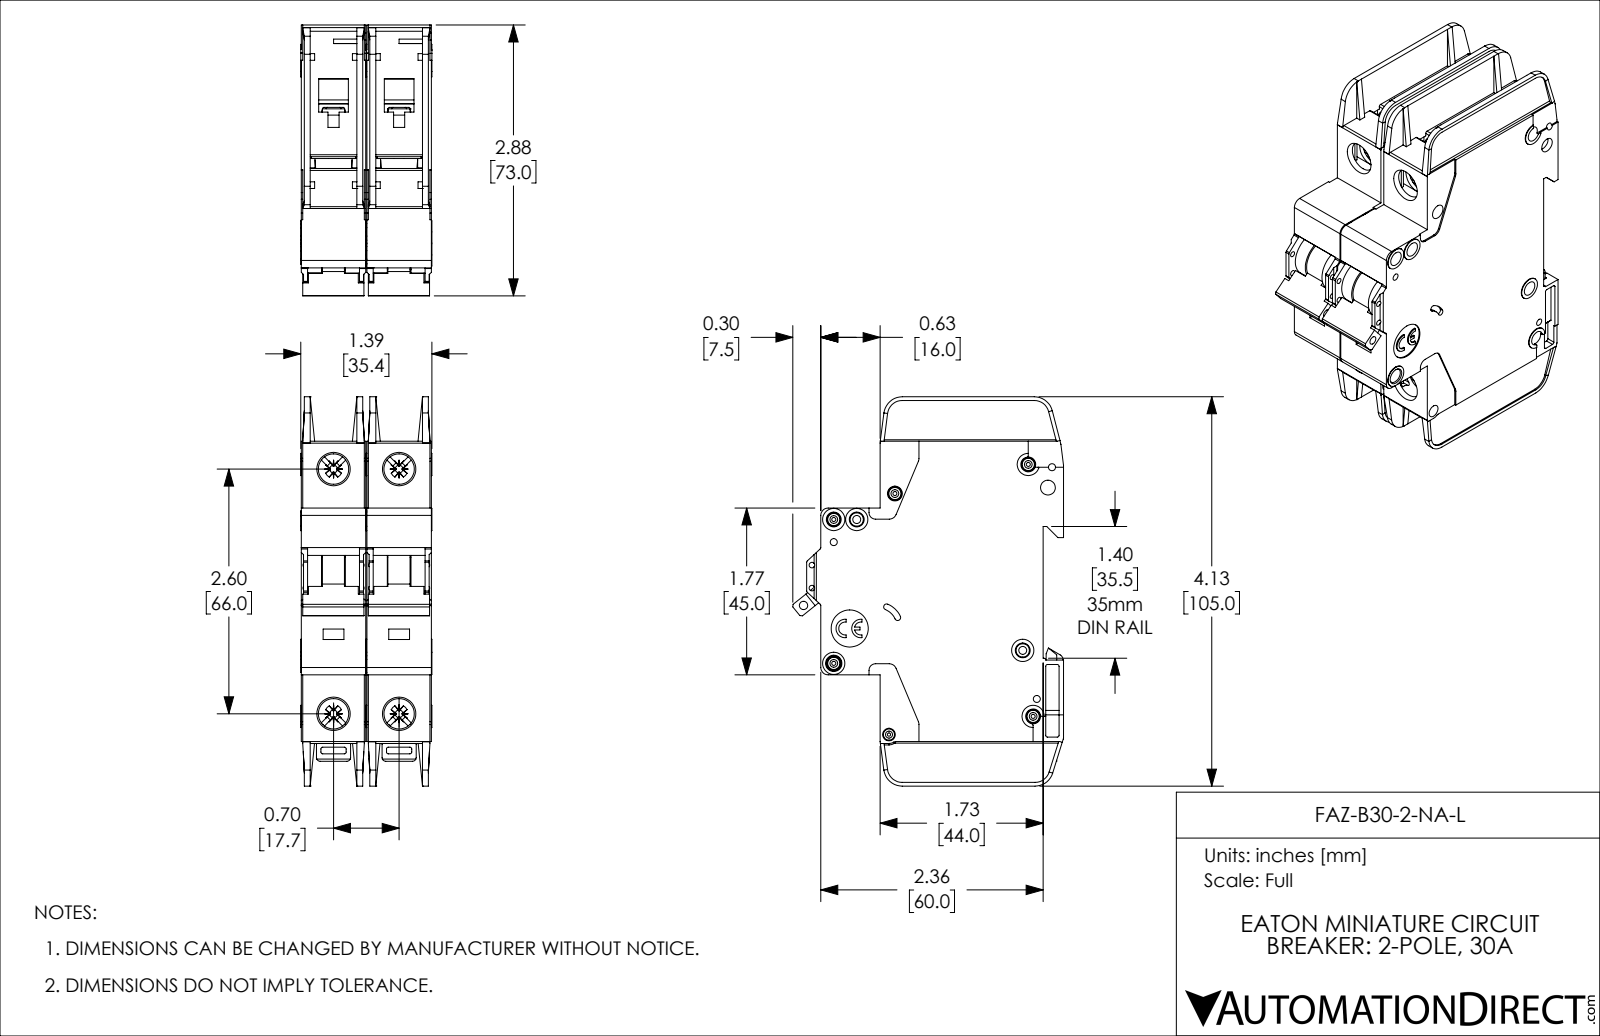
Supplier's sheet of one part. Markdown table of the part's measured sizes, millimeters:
| quantity | value |
| --- | --- |
| part name | FAZ-B30-2-NA-L |
| STEP written by | SolidWorks 2019 (AUTOMOTIVE_DESIGN) |
| units | millimeters |
| bodies | 2 solids, 2254 faces (1342 planar, 714 cylindrical, 198 other) |
| overall size | 105 × 73.1 × 35.4 |
| volume | 153 500 mm³ |
| surface area | 52 910 mm² |
| round holes (diameter × count) | 4 × 8, 1.1 × 5, 1.9 × 4, 8.2 × 4, 1.5 × 2, 2.2 × 2, 0.9 × 1, 2.3 × 1, 2.5 × 1, 3.4 × 1, 10 × 1 |
| round bosses / shafts (diameter × count) | 3.3 × 5, 6 × 4, 3 × 3, 2.5 × 2 |
| partial cylindrical surfaces (radius × count) | 0.5 × 57, 0.4 × 20, 1 × 14, 2 × 10, 1.1 × 8, 0.2 × 5, 5 × 5, 0.3 × 4 |
| main face-to-face distances | 17.7, 1.2, 17.4, 15, 2.4, 16.2, 13.8, 35.1, 18.9, 16.5 |
| hole center spacings | 6.2, 13.6, 17.7, 22.1, 66, 68.3, 4.8, 5.1 |
